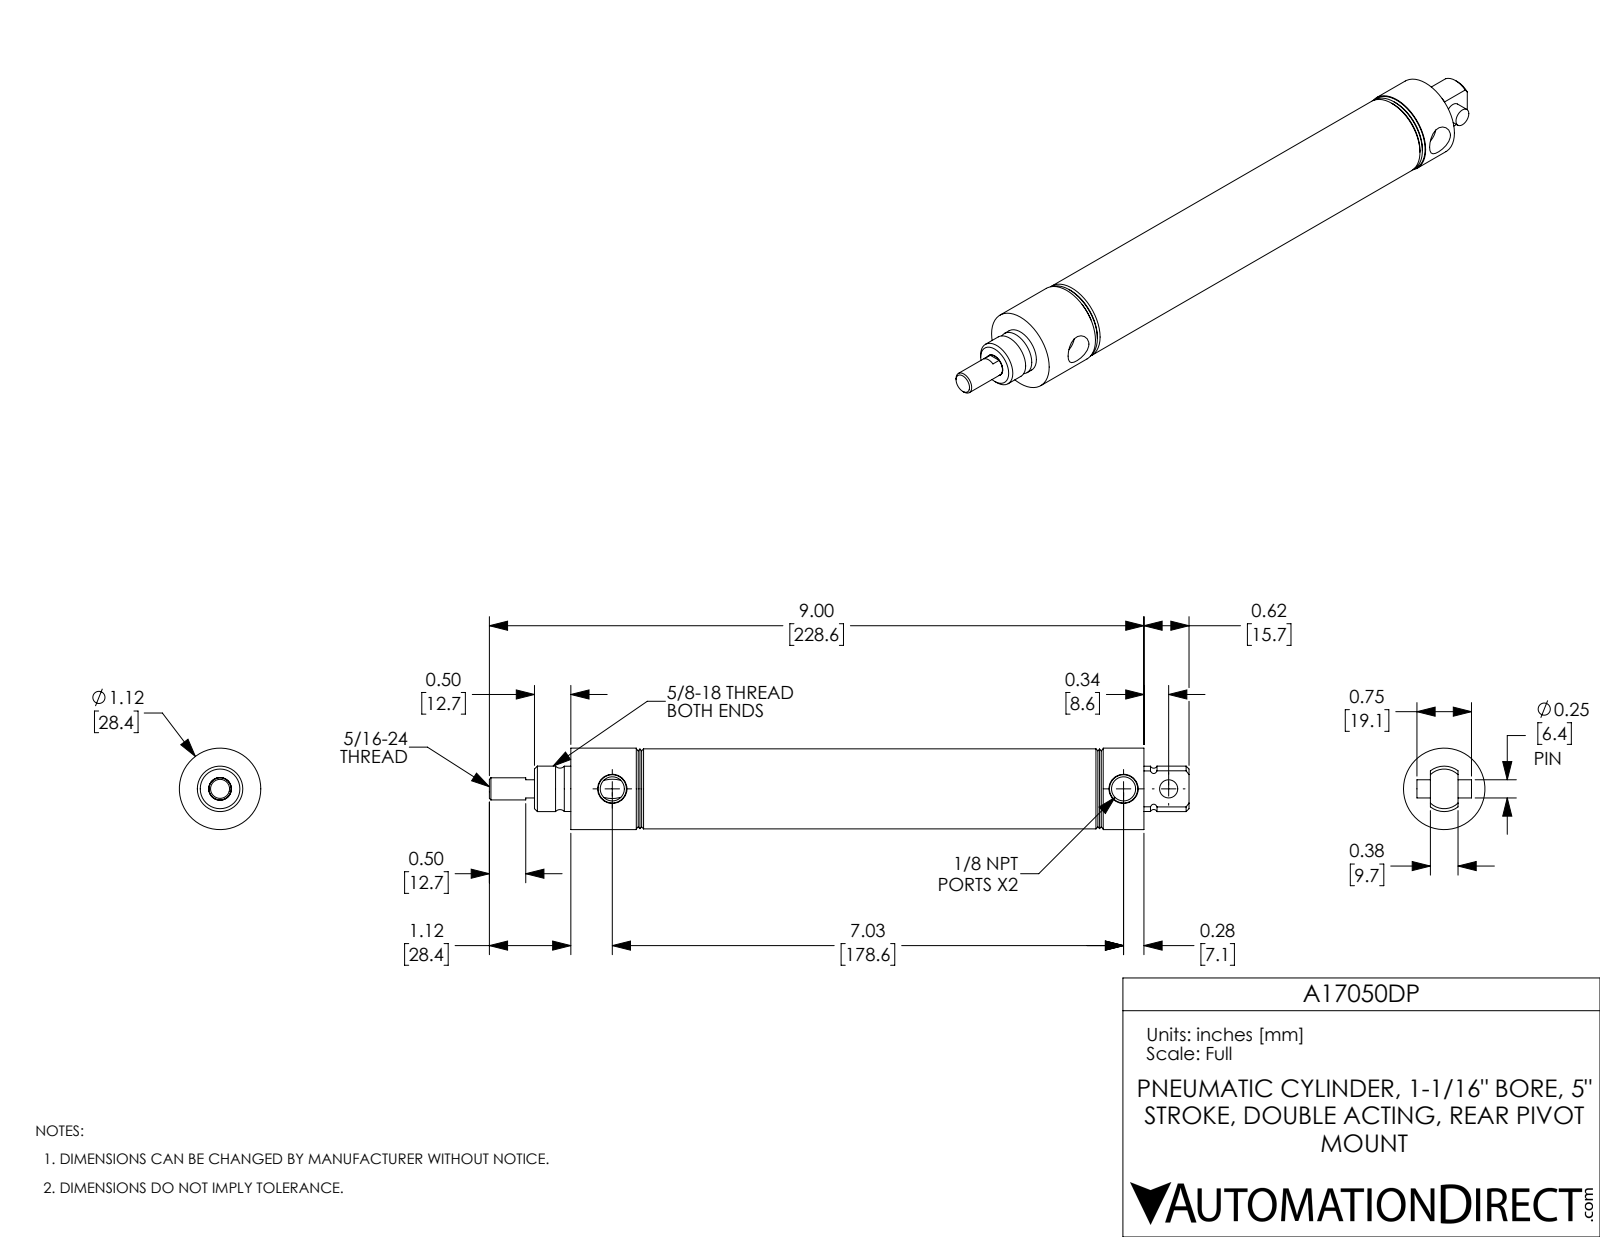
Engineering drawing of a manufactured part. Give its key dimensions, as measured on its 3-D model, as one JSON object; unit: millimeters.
{"part_name": "A17050DP-MainBody; A17050DP-Rod; A17050DP-PIN; A17050DP", "step_written_by": "SolidWorks 2017 (AUTOMOTIVE_DESIGN)", "units": "millimeters", "bodies": {"solids": 3, "faces": 92, "planar": 22, "cylindrical": 32, "other": 38}, "overall_size": [244.3, 28.4, 28.4], "volume_mm3": 61070, "surface_area_mm2": 42340, "round_holes": [[8.4, 2], [6.4, 1], [7.9, 1], [27, 1]], "round_bosses_or_shafts": [[28.4, 1], [27.9, 1], [15.9, 1], [15.8, 1], [7.7, 1]], "partial_cylinders_radius": [[8, 1]], "face_to_face_distances": [12.7, 169.9, 139.7, 127, 30.2, 42.9, 169.9, 200.2, 157.2, 30.2], "hole_center_spacings": [15.7, 178.6, 194.3]}
